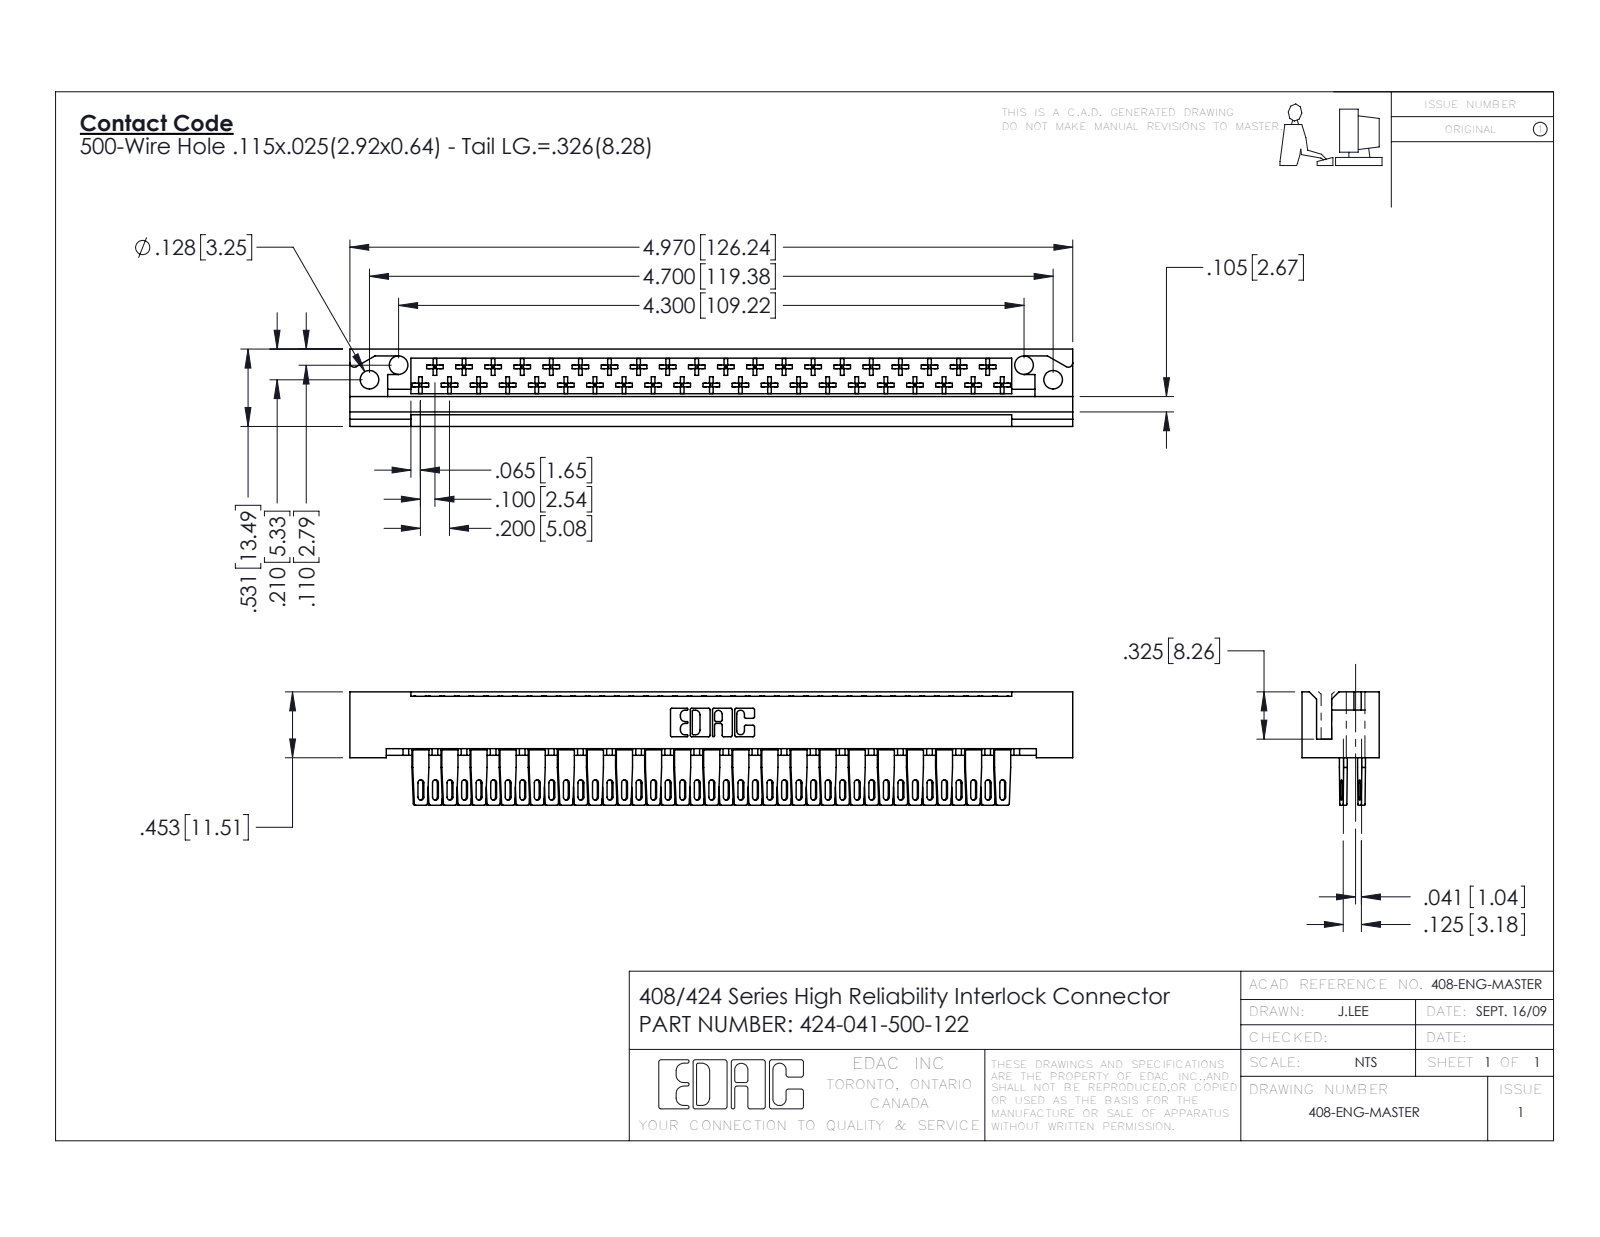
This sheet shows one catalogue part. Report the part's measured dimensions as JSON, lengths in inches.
{"part_name": "424 Part_041; 424-047-500-122; 408-290-001_408-290-100", "step_written_by": "SolidWorks 2016 (CONFIG_CONTROL_DESIGN)", "units": "inches", "bodies": {"solids": 42, "faces": 2482, "planar": 1770, "cylindrical": 548, "other": 164}, "overall_size": [4.97, 0.779, 0.531], "volume_in3": 0.821, "surface_area_in2": 29.08, "round_holes": [[0.128, 4]], "partial_cylinders_radius": [[0.01, 328], [0.021, 82], [0.02, 43], [0.01, 22], [0.007, 6], [0.031, 6], [0.026, 3], [0.03, 2]], "face_to_face_distances": [0.1, 0.296, 0.025, 0.531, 0.125, 0.235, 0.259, 0.272, 0.025, 0.326], "hole_center_spacings": [0.224, 4.501, 4.3, 4.7]}
